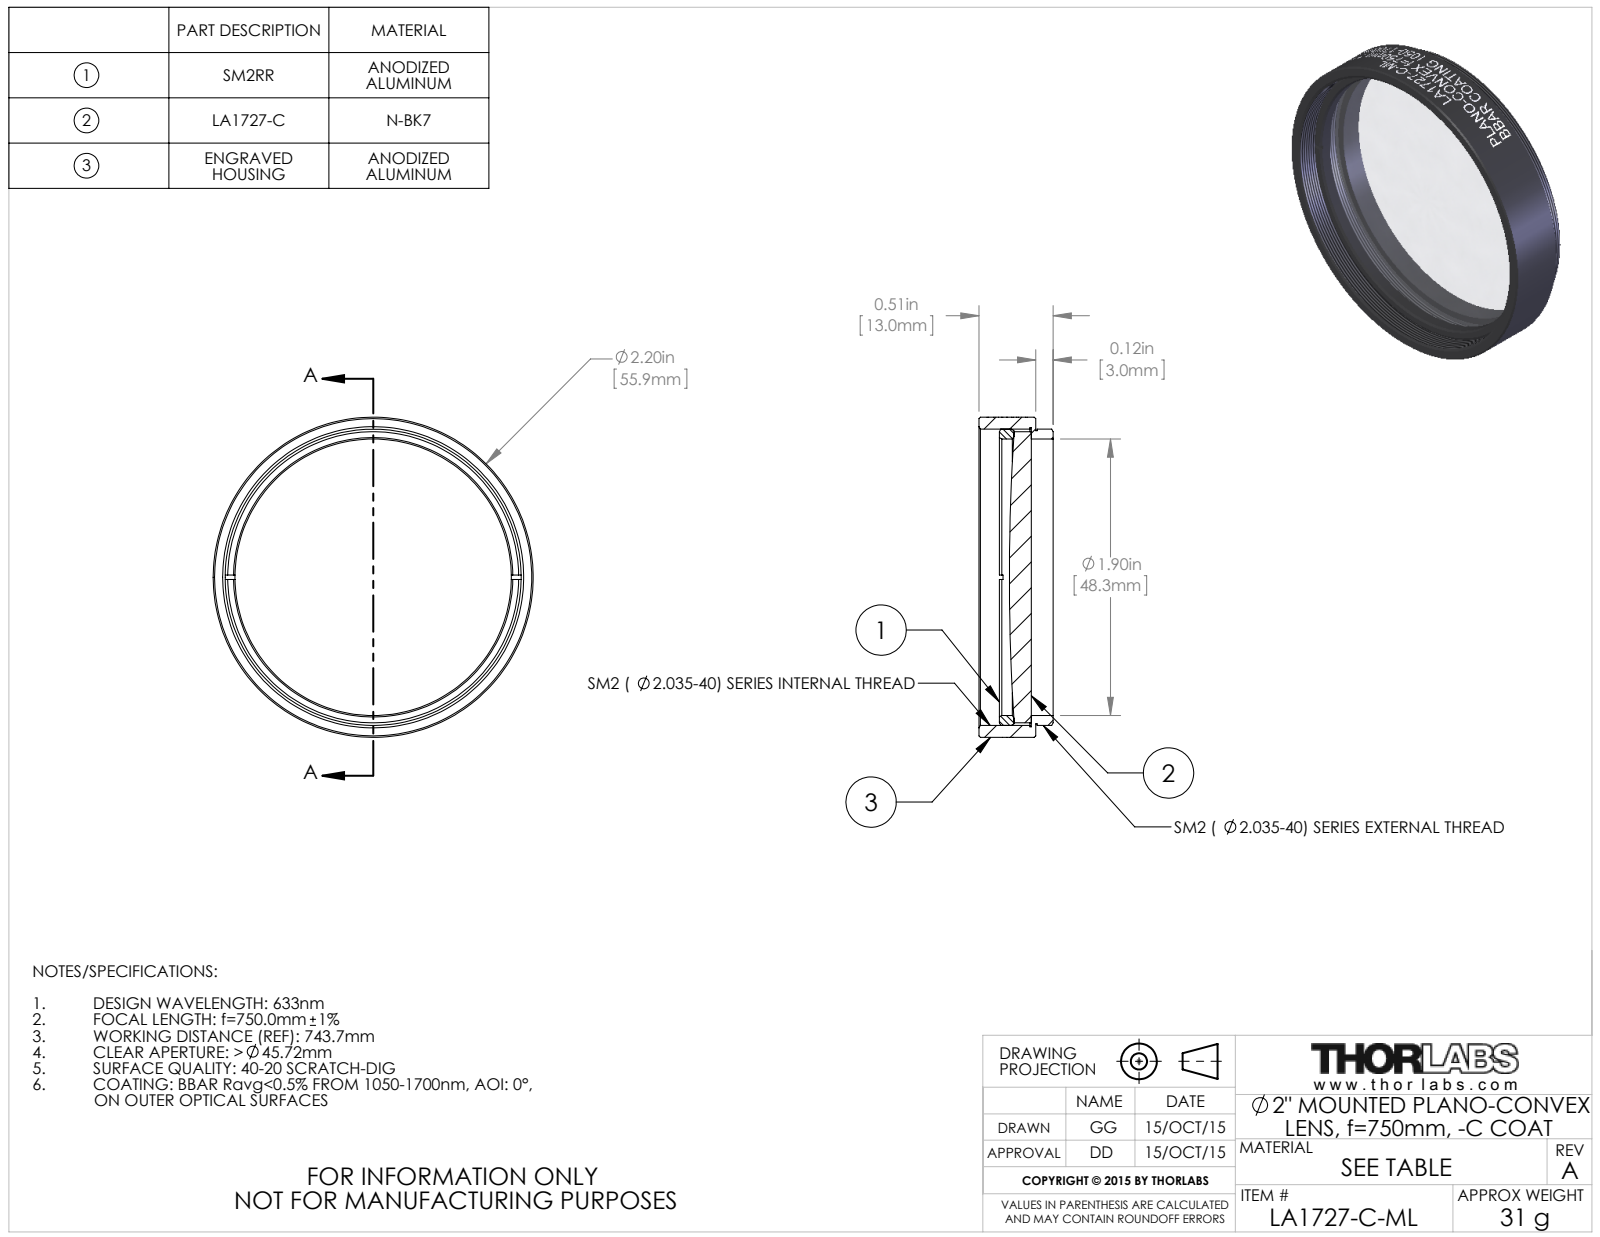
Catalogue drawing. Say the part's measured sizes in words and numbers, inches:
The part is named "TTN039627-E0W". Its 3-D file was written by "SolidWorks 2014 (CONFIG_CONTROL_DESIGN)". It is 3 solids with 146 faces: 16 planar, 106 cylindrical and 24 other. Overall it measures 2.2 by 2.2 by 0.51 inches. Its volume is 0.735 cubic inches and its surface area 17.57 square inches. Round holes: 1 of diameter 1.9, 1 of diameter 2.055. Round bosses or shafts: 1 of diameter 2.2, 1 of diameter 2.035, 1 of diameter 2.015, 1 of diameter 2. The main face-to-face distances are 0.12, 0.15, 0.03, 0.39, 0.36, 0.51, 0.27, 0.24, 0.37, 0.25.
